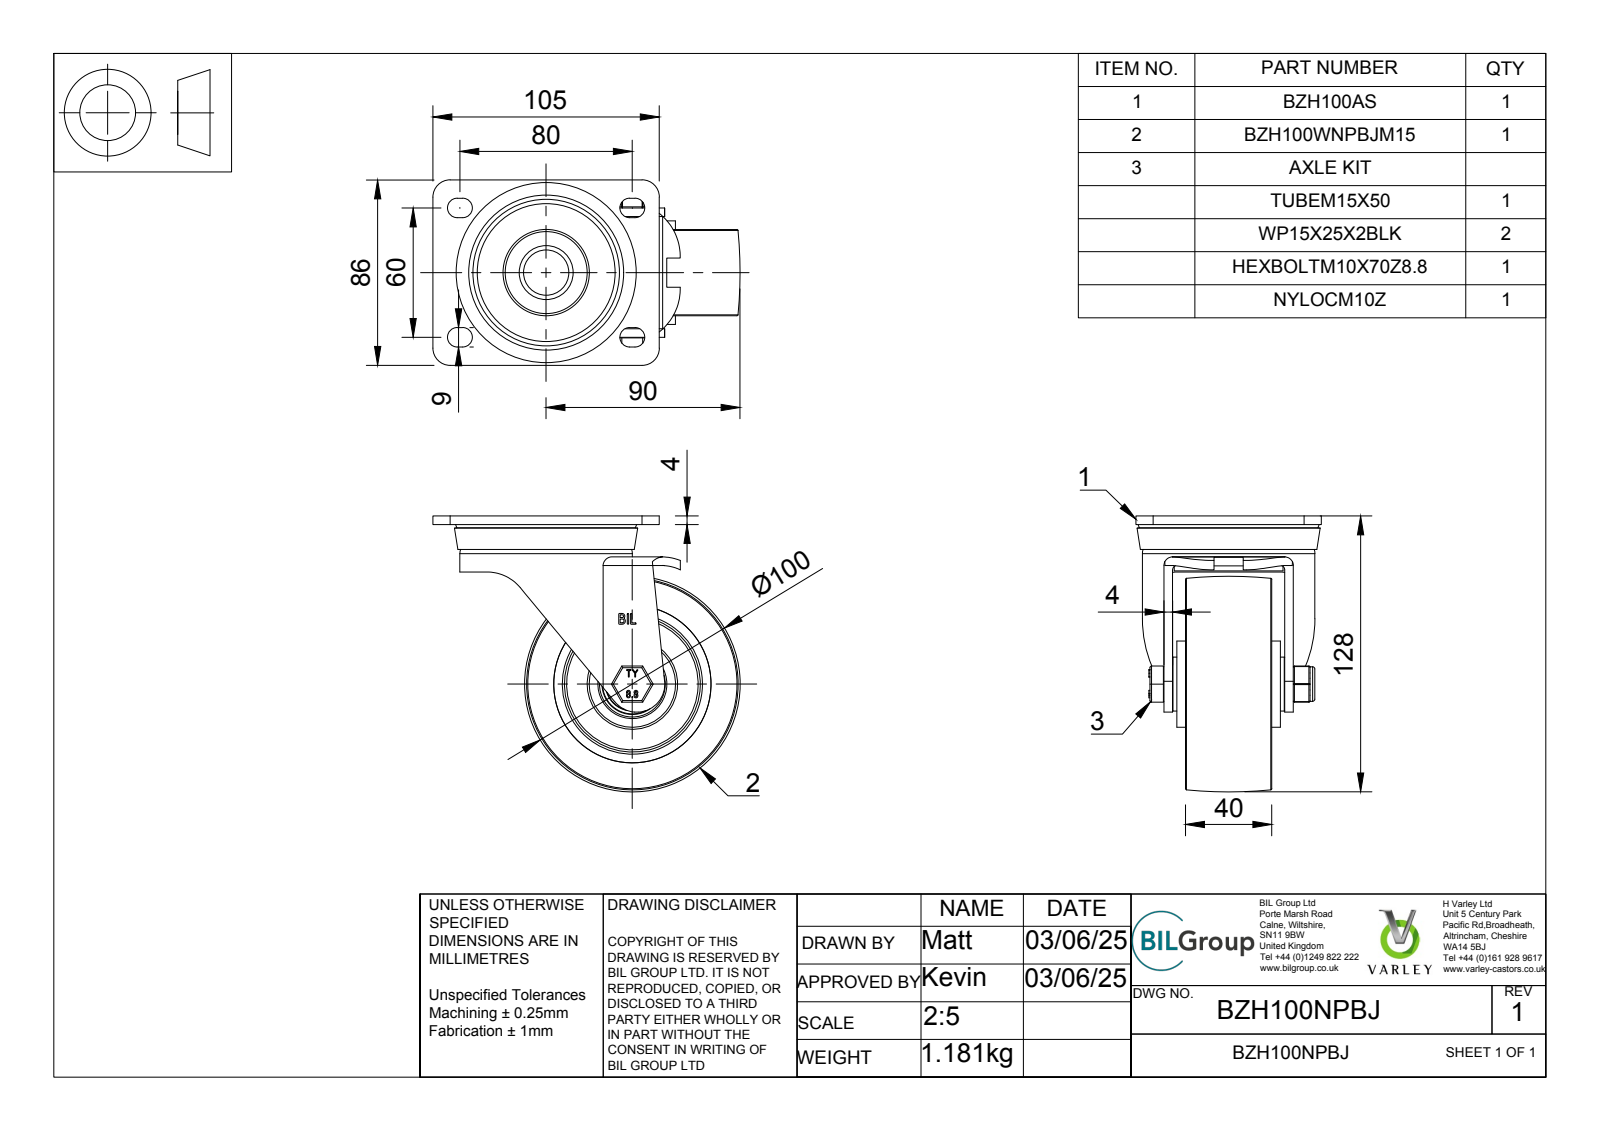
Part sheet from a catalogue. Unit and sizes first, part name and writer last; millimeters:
Units: millimetres
Overall size (bounding box): 142.5 × 128 × 86
Round holes (diameter × count): ⌀32 ×2, ⌀10 ×1, ⌀10.2 ×1, ⌀10.5 ×1, ⌀12 ×1, ⌀15 ×1, ⌀15.75 ×1, ⌀20.5 ×1, ⌀25 ×1, ⌀26.8 ×1, ⌀28 ×1, ⌀28.2 ×1
Round bosses / shafts (diameter × count): ⌀20 ×2, ⌀80 ×1, ⌀50.5 ×1, ⌀40 ×1, ⌀31 ×1, ⌀25 ×1, ⌀21.5 ×1, ⌀19 ×1
Partial cylindrical surfaces — rounded edges, fillets, slot ends (radius × count): R0.5 ×18, R4.5 ×8, R0.75 ×6, R2 ×4, R8 ×4, R4 ×2, R25.41 ×2, R11.4 ×1
Main face-to-face distances: 4, 6, 50, 11.5, 7.5, 5, 40, 10, 46, 17.5
Volume: 371 318 mm³ · Surface area: 150 684 mm²
Bodies: 40 solids, 1148 faces (423 planar, 195 cylindrical, 530 other)
Part name (STEP PRODUCT): BZH100NPBJ v5; BZH100WNPBJM15 v1; POLYURETHANE TYRE; NYLON RIM (+7 more)
STEP written by: Autodesk Translation Framework v14.10.0.0 (AUTOMOTIVE_DESIGN)
